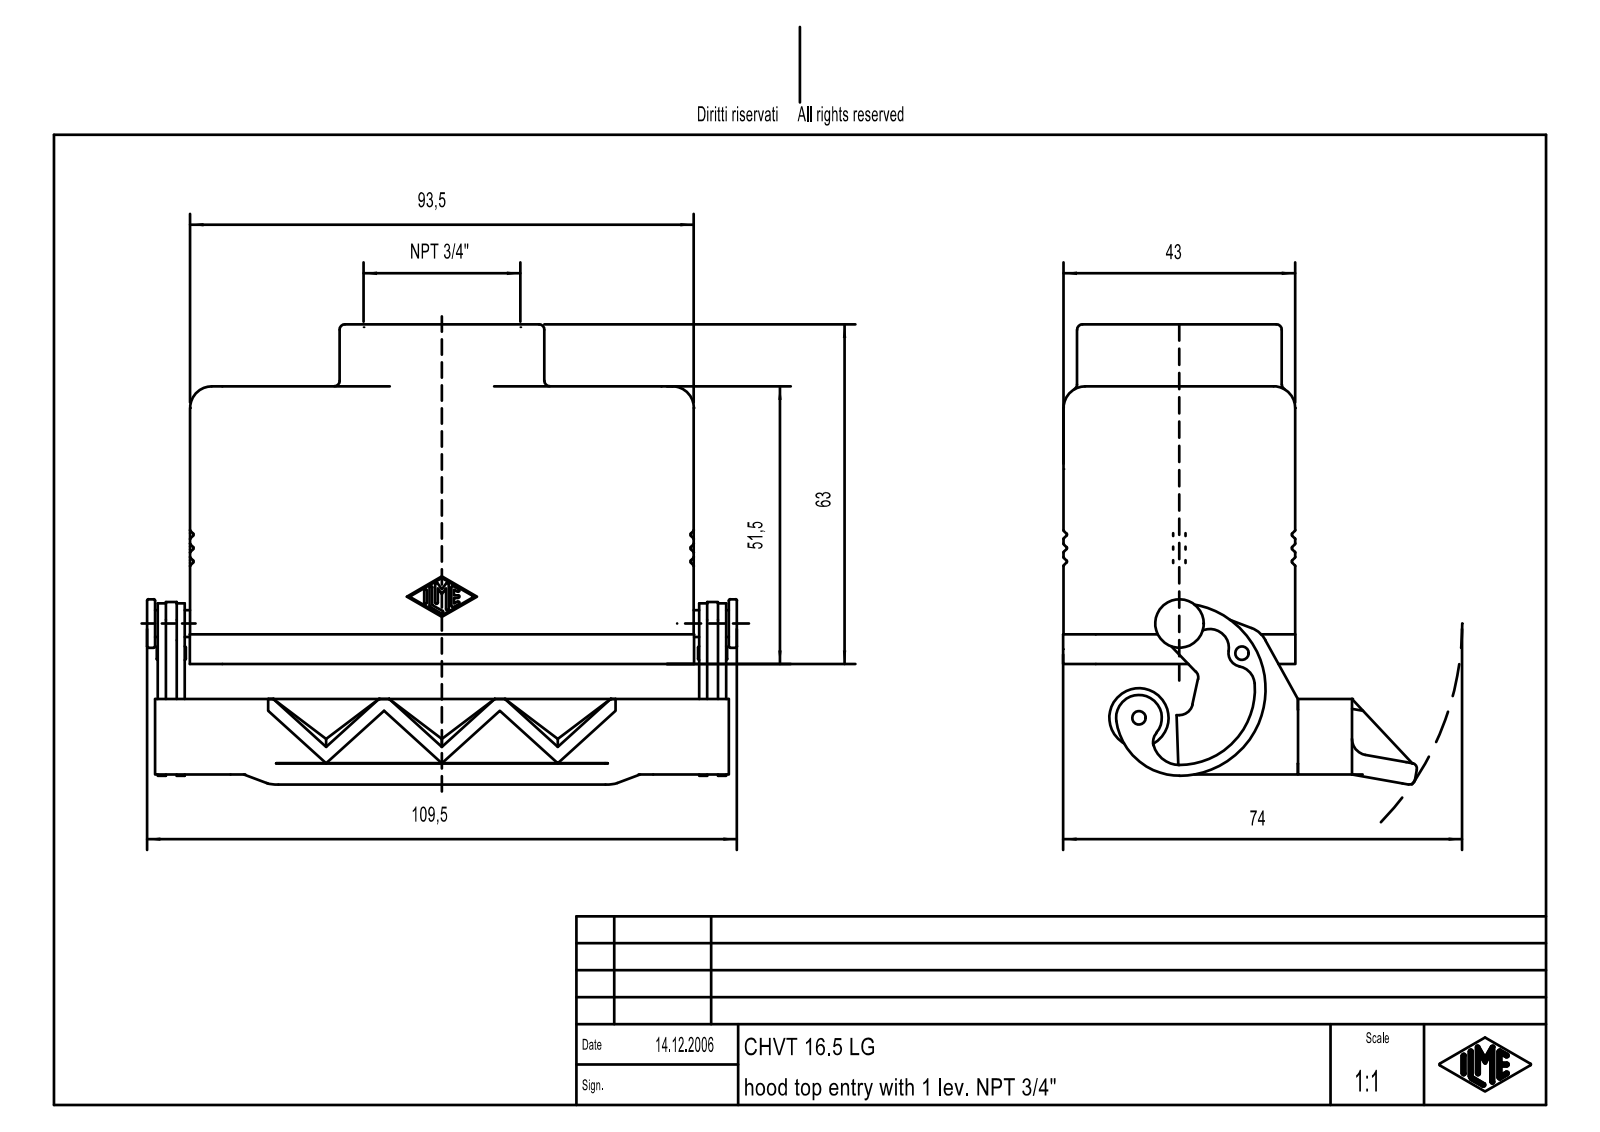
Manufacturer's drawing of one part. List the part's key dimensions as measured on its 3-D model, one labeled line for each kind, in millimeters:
Part name (STEP PRODUCT): MSBO12851
STEP written by: Creo Elements/Direct Modeling 18.0B 02-Dec-2011 (C) Parametric Technology GmbH (AUTOMOTIVE_DESIGN)
Units: millimetres
Bodies: 1 solid, 646 faces (272 planar, 214 cylindrical, 160 other)
Overall size (bounding box): 109.5 × 85.37 × 65.64
Volume: 87 961 mm³ · Surface area: 46 630 mm²
Round holes (diameter × count): ⌀2.01 ×4, ⌀3.1 ×4, ⌀2.5 ×1
Round bosses / shafts (diameter × count): ⌀38 ×1, ⌀11 ×1, ⌀9 ×1, ⌀5 ×1, ⌀3.1 ×1, ⌀2 ×1
Partial cylindrical surfaces — rounded edges, fillets, slot ends (radius × count): R0.2 ×28, R0.25 ×26, R2.5 ×9, R1 ×6, R1.5 ×5, R4 ×5, R2.45 ×4, R6 ×4
Main face-to-face distances: 3.5, 39.5, 36, 43, 3.55, 90, 4.5, 8, 4, 2
Hole centre spacings: 27, 77.5, 82.07
